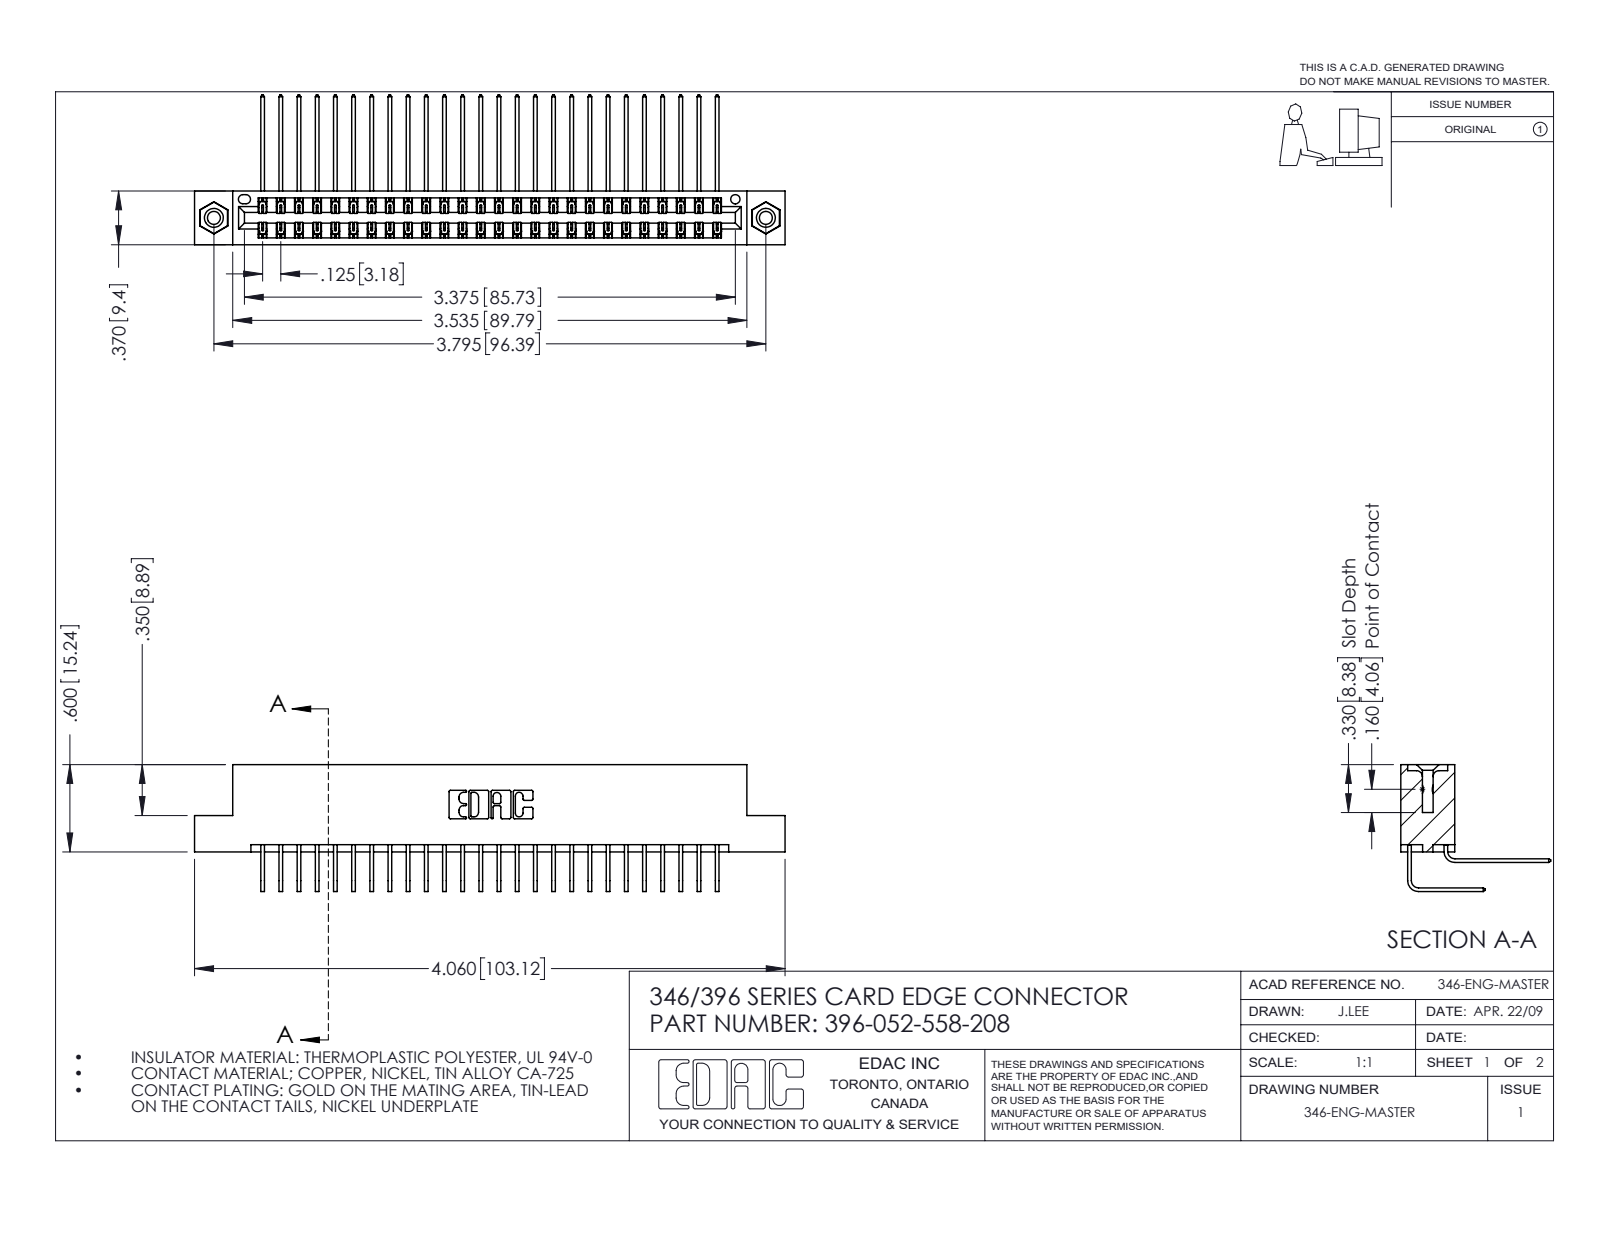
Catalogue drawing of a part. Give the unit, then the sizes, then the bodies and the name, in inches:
Units: inches
Overall size (bounding box): 4.06 × 1.03 × 0.873
Round holes (diameter × count): ⌀0.089 ×2, ⌀0.125 ×2, ⌀0.156 ×2, ⌀0.064 ×1
Round bosses / shafts (diameter × count): ⌀0.155 ×2
Partial cylindrical surfaces — rounded edges, fillets, slot ends (radius × count): R0.006 ×78, R0.01 ×22, R0.007 ×6, R0.031 ×6, R0.026 ×3, R0.014 ×2, R0.022 ×2, R0.024 ×2
Main face-to-face distances: 0.048, 0.322, 0.025, 0.25, 0.37, 0.072, 0.298, 0.275, 0.148, 0.222
Hole centre spacings: 0.246, 3.587, 3.795
Volume: 0.624 in³ · Surface area: 23.66 in²
Bodies: 55 solids, 2990 faces (2032 planar, 942 cylindrical, 16 other)
Part name (STEP PRODUCT): 396-052-558-208; 345-292-001_558 559 Tail - 1; 346 Part_Flush Mounting Lugs - 0.156 Dia-TI; 345-292-001_558 Tail - 2 (+1 more)
STEP written by: SolidWorks 2016 (CONFIG_CONTROL_DESIGN)
